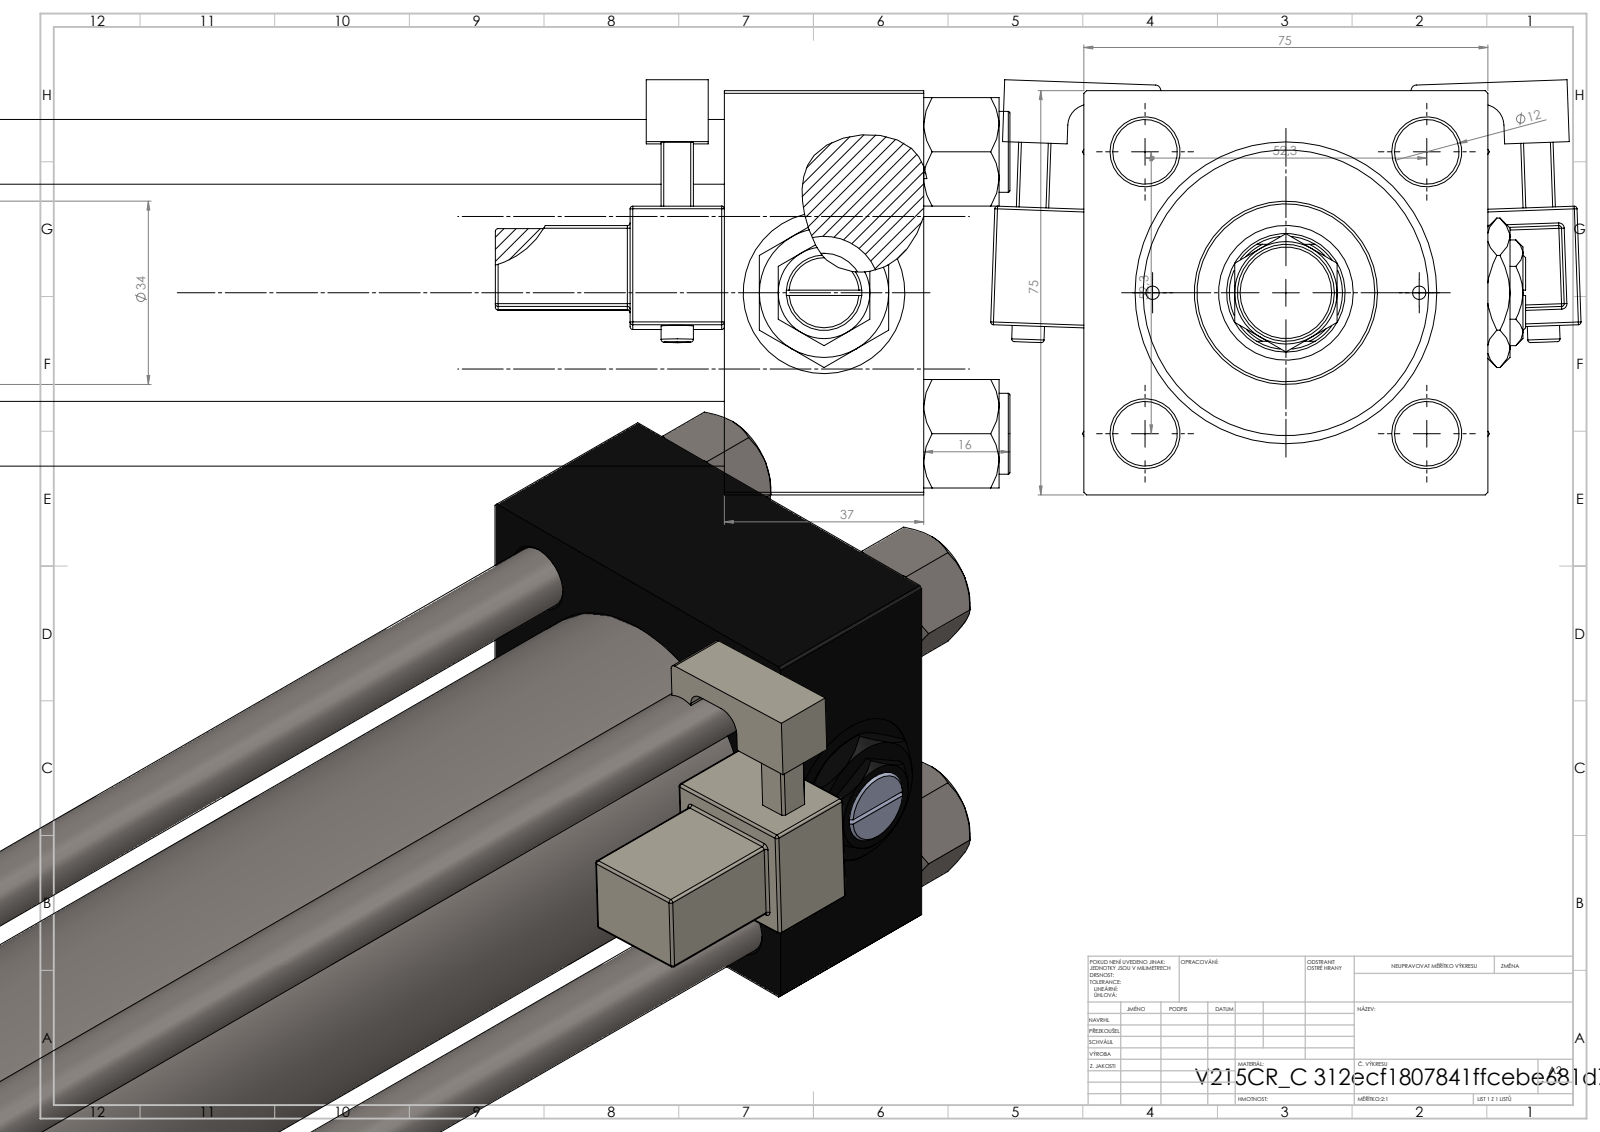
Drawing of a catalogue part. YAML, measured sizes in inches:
part_name: "V215CR_C_Body; Zatka_pro_OIL_PORT; V215_VC_A; MFA (+4 more)"
step_written_by: "SolidWorks 2019 (CONFIG_CONTROL_DESIGN)"
units: inches
bodies: {solids: 16, faces: 1461, planar: 649, cylindrical: 166, other: 646}
overall_size: [27.874, 4.314, 3.033]
volume: 81.77
surface_area: 669.9
round_holes:
  - {diameter: 0.472, count: 4}
  - {diameter: 0.098, count: 2}
  - {diameter: 0.276, count: 2}
  - {diameter: 0.825, count: 2}
  - {diameter: 1.181, count: 2}
  - {diameter: 0.413, count: 1}
  - {diameter: 0.866, count: 1}
  - {diameter: 0.984, count: 1}
  - {diameter: 1.614, count: 1}
  - {diameter: 1.969, count: 1}
  - {diameter: 2.087, count: 1}
round_bosses_or_shafts:
  - {diameter: 0.591, count: 4}
  - {diameter: 0.236, count: 2}
  - {diameter: 2.205, count: 1}
  - {diameter: 1.339, count: 1}
  - {diameter: 0.709, count: 1}
  - {diameter: 0.433, count: 1}
partial_cylinders:
  - {radius: 0.02, count: 48}
  - {radius: 0.039, count: 2}
  - {radius: 0.098, count: 2}
  - {radius: 0.157, count: 2}
  - {radius: 0.413, count: 1}
face_to_face_distances: [2.953, 1.457, 24.961, 23.504, 22.638, 21.181, 2.323, 23.831, 22.374, 1.193]
hole_center_spacings: [1.031, 1.456, 2.059, 2.253, 0.974, 2.912, 1.949, 22.579]
